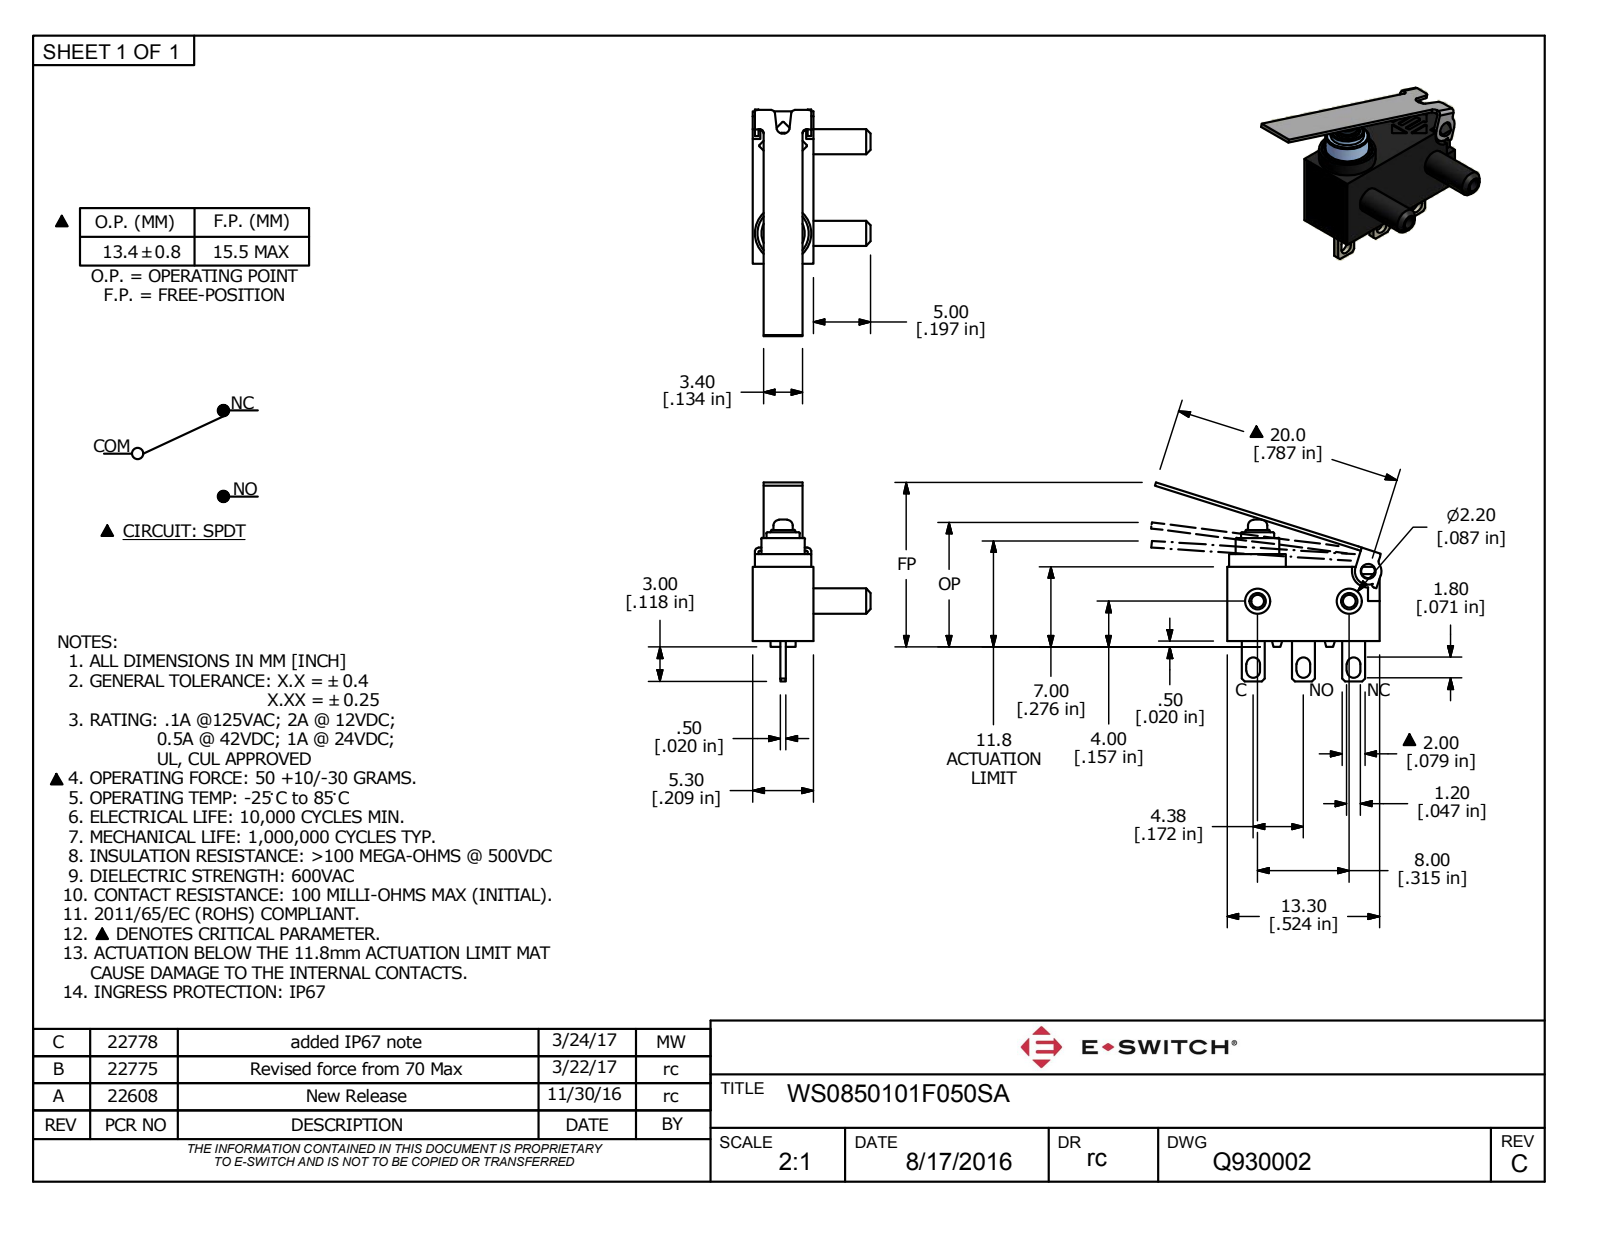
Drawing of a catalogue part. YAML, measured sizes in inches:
part_name: "P:\\\\E-Switch Secure\\\\3D_MODELS_STP_FORMAT\\\\WS0850101F050SA.stp"
step_written_by: "ACIS (CONFIG_CONTROL_DESIGN)"
units: inches
bodies: {solids: 2, faces: 189, planar: 121, cylindrical: 59, other: 9}
overall_size: [0.778, 0.684, 0.406]
volume: 0.034
surface_area: 1.195
round_holes:
  - {diameter: 0.043, count: 2}
  - {diameter: 0.051, count: 1}
  - {diameter: 0.177, count: 1}
round_bosses_or_shafts:
  - {diameter: 0.087, count: 2}
  - {diameter: 0.195, count: 1}
  - {diameter: 0.15, count: 1}
  - {diameter: 0.114, count: 1}
  - {diameter: 0.067, count: 1}
partial_cylinders:
  - {radius: 0.024, count: 7}
  - {radius: 0.012, count: 6}
  - {radius: 0.004, count: 2}
  - {radius: 0.01, count: 2}
  - {radius: 0.018, count: 2}
  - {radius: 0.045, count: 1}
  - {radius: 0.055, count: 1}
face_to_face_distances: [0.209, 0.256, 0.094, 0.114, 0.524, 0.02, 0.018, 0.163, 0.252, 0.171]
hole_center_spacings: [0.121, 0.315, 0.393]
